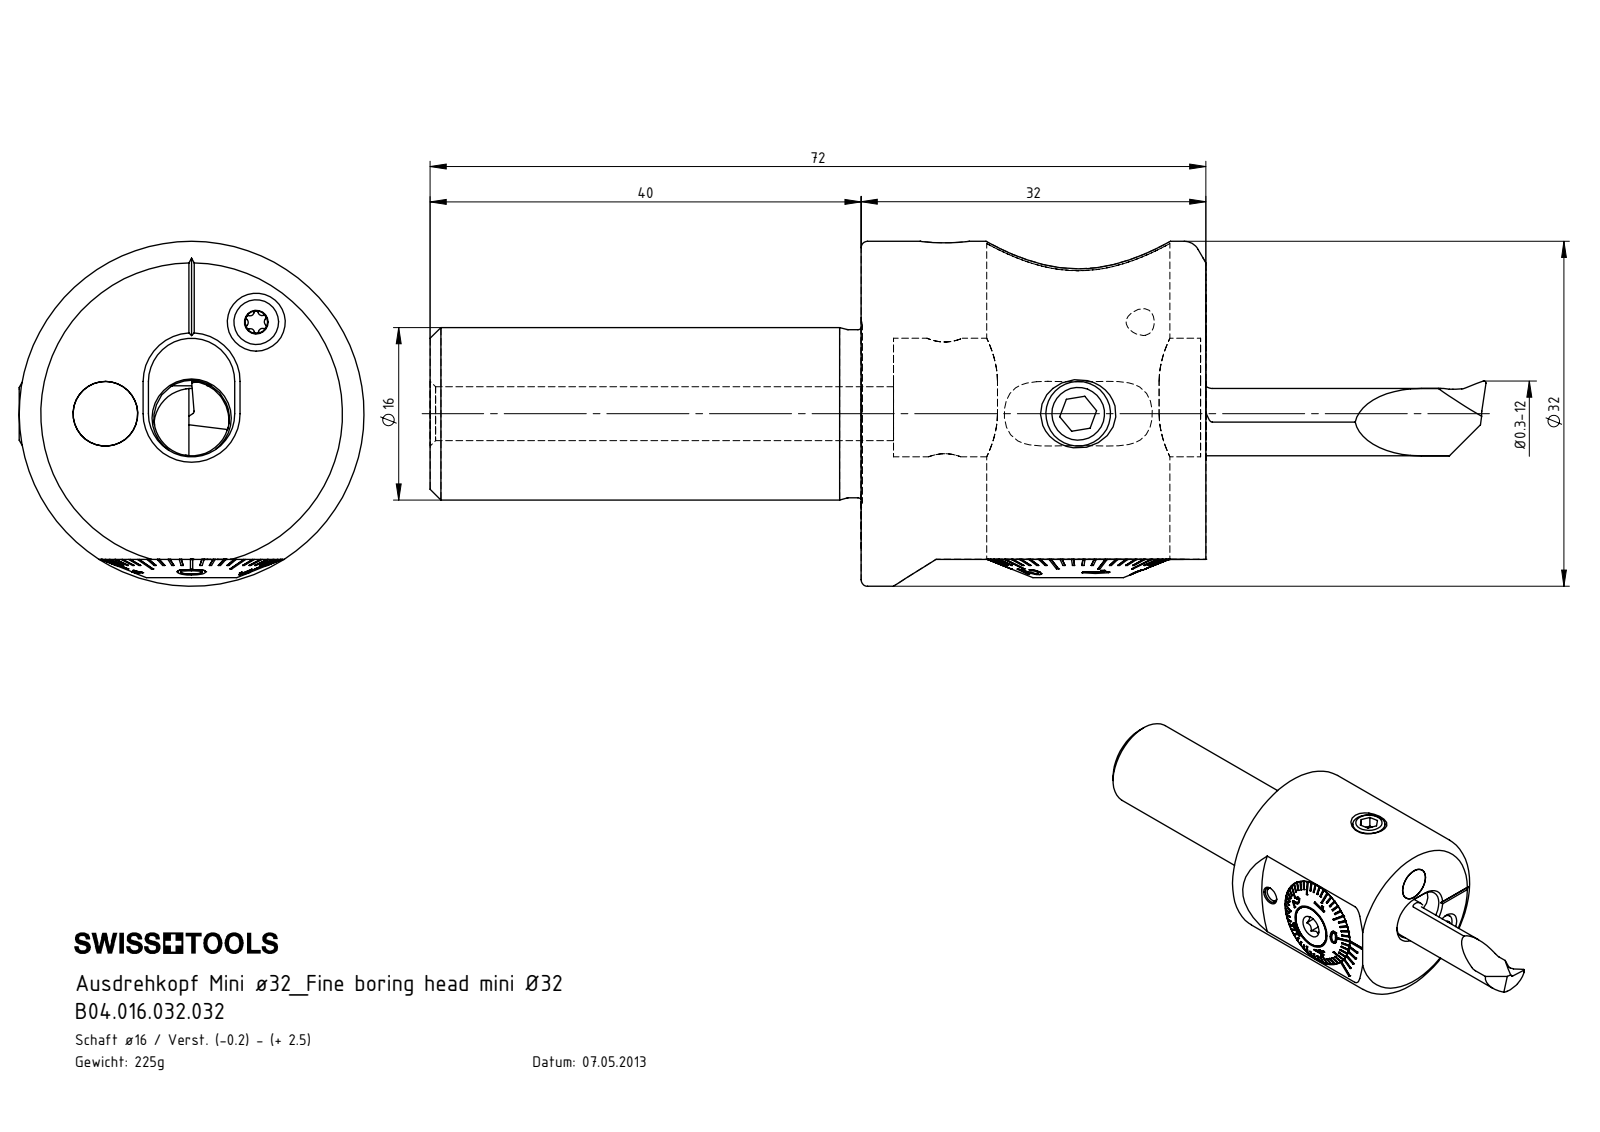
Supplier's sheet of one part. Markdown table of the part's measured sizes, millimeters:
| quantity | value |
| --- | --- |
| part name | F32-BG2.017.003_A; DIN 3771 - 15x1; A32-BG2.014.010_A; F32-BG2.017.004_A (+8 more) |
| STEP written by | SolidWorks 2017 (CONFIG_CONTROL_DESIGN) |
| units | millimeters |
| bodies | 16 solids, 733 faces (310 planar, 142 cylindrical, 281 other) |
| overall size | 98 × 32 × 32 |
| volume | 30 597 mm³ |
| surface area | 16 872 mm² |
| round holes (diameter × count) | 5 × 8, 3.3 × 2, 1 × 1, 2 × 1, 2.5 × 1, 2.9 × 1, 3 × 1, 6 × 1, 7 × 1, 7.75 × 1, 8.4 × 1, 10.2 × 1 |
| round bosses / shafts (diameter × count) | 6 × 3, 32 × 1, 17 × 1, 16.98 × 1, 16.85 × 1, 16 × 1, 15.6 × 1, 14.65 × 1 |
| partial cylindrical surfaces (radius × count) | 0.21 × 6, 0.36 × 5, 0.2 × 4, 2.2 × 4, 4 × 2, 0.36 × 1, 0.5 × 1, 1.9 × 1 |
| main face-to-face distances | 32, 4.5, 3.7, 0.8, 1.5, 2.2, 2.3, 3, 40, 72 |
| hole center spacings | 4.5, 10.4, 11.88, 12.21, 0.4, 7.9, 8, 8.01 |
